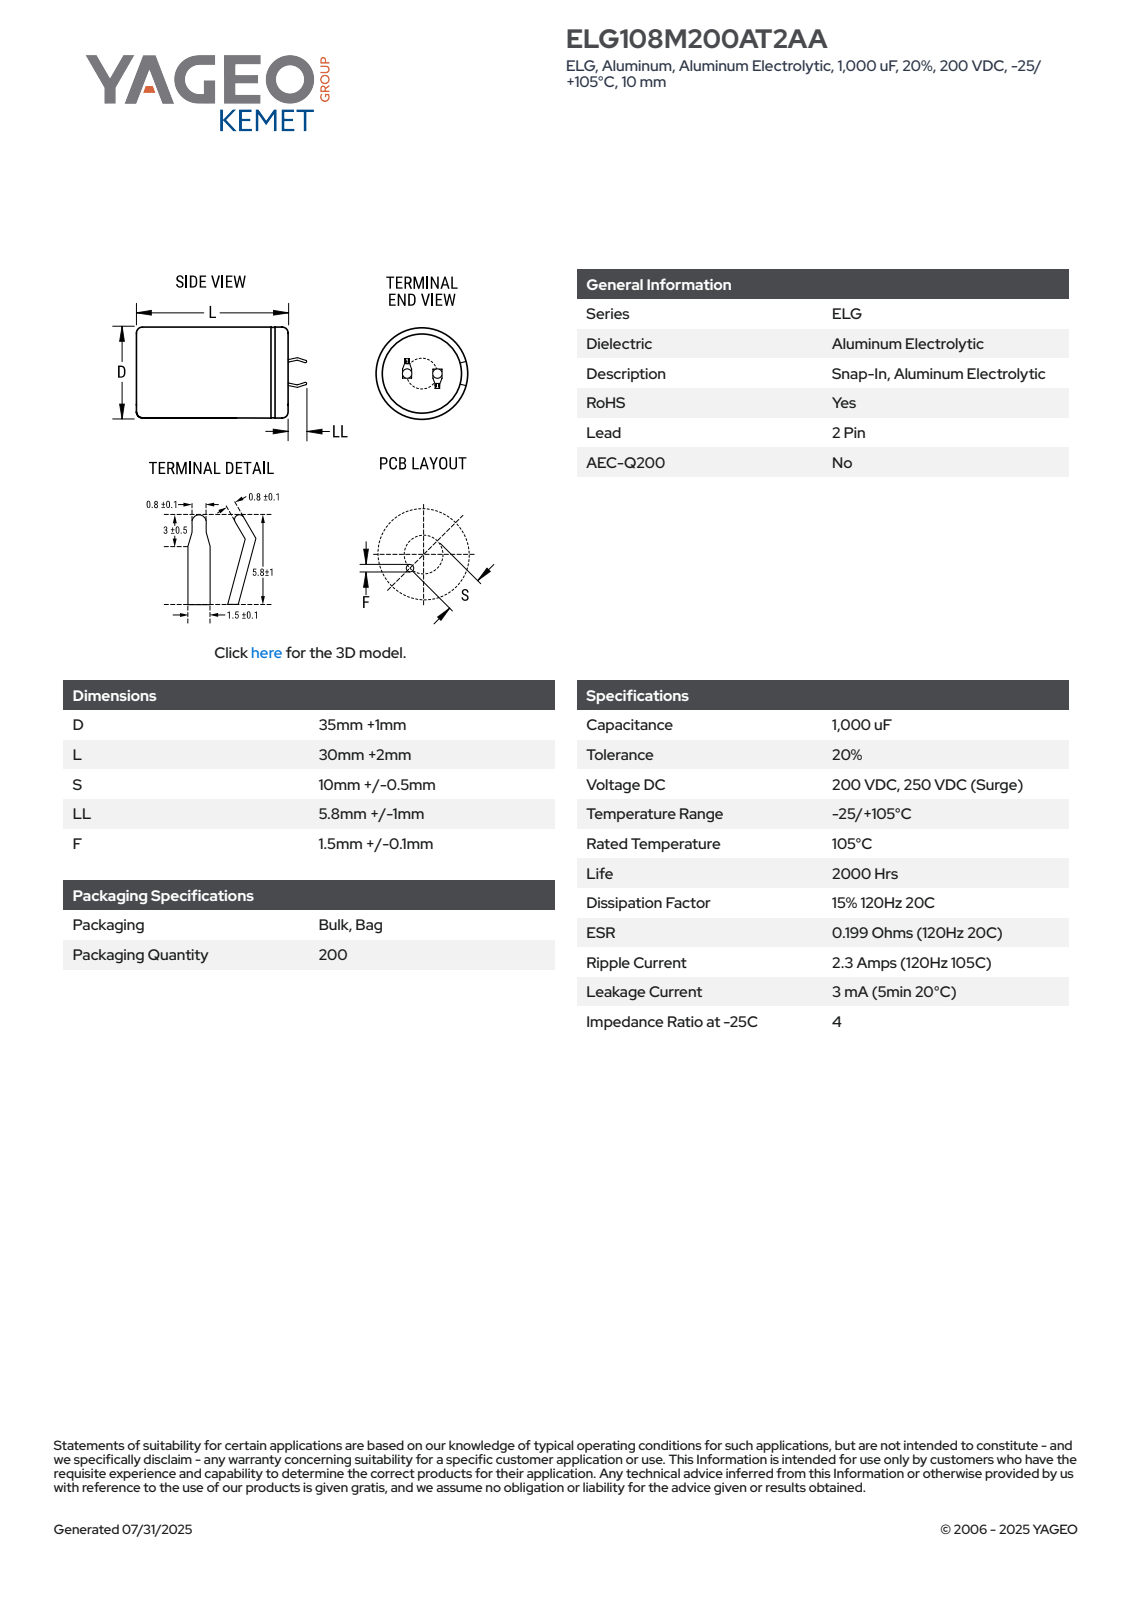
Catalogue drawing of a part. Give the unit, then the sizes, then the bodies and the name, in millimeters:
Units: millimetres
Overall size (bounding box): 38.79 × 36 × 36
Round holes (diameter × count): ⌀31.85 ×1
Round bosses / shafts (diameter × count): ⌀36 ×1
Partial cylindrical surfaces — rounded edges, fillets, slot ends (radius × count): R17.99 ×1
Main face-to-face distances: 31.99, 0.6, 32.49, 0.5, 7.08, 7.63, 0.75, 1.35, 7.68, 6.48
Volume: 32 044 mm³ · Surface area: 5 650 mm²
Bodies: 1 solid, 100 faces (52 planar, 9 cylindrical, 39 other)
Part name (STEP PRODUCT): CARS_K2P_35X30_D36L32S10LL6.8F1.6
STEP written by: SolidWorks 2014 (AUTOMOTIVE_DESIGN)
